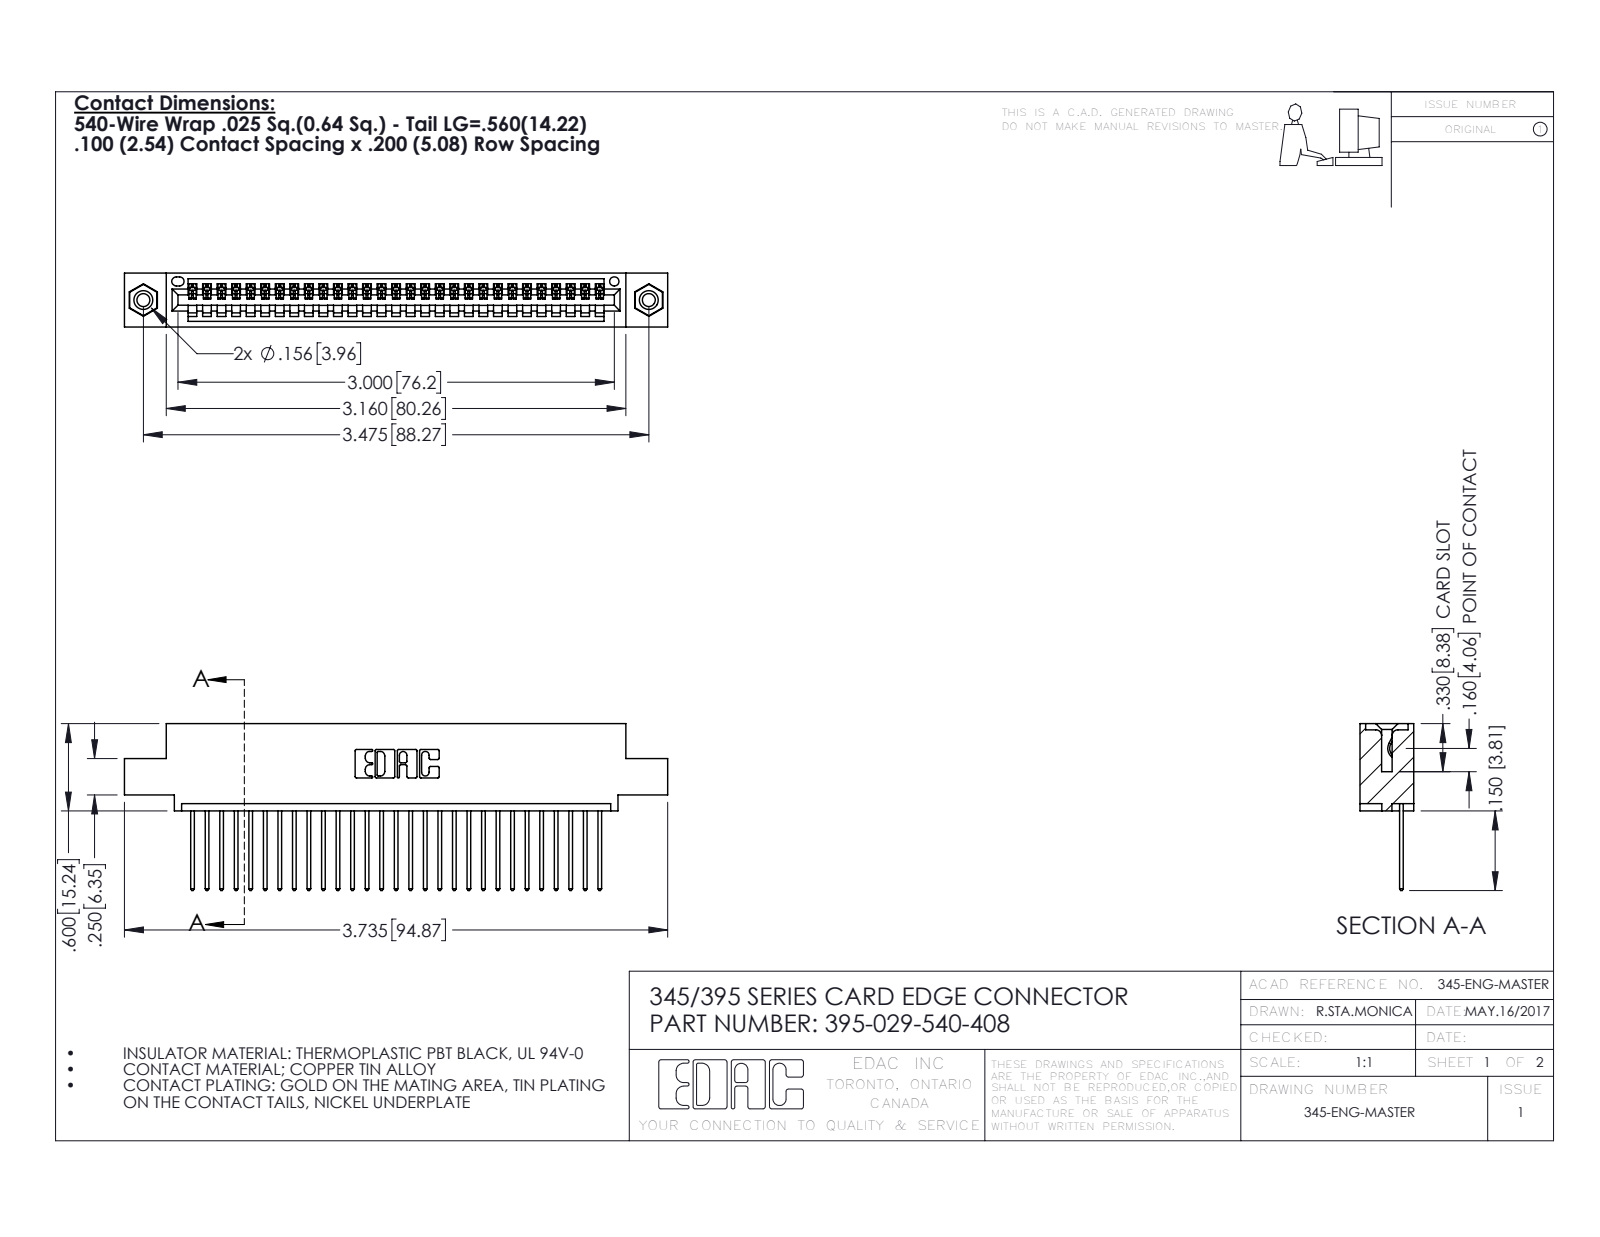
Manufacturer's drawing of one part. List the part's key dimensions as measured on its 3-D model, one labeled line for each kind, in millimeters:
Part name (STEP PRODUCT): 345-292-001_345-293-140; 395-029-540-408; 345-250-001_345-250-003-102; 345 Part_0.110 Offset - 0.156 Dia-TI
STEP written by: SolidWorks 2016 (CONFIG_CONTROL_DESIGN)
Units: millimetres
Bodies: 32 solids, 1872 faces (1276 planar, 580 cylindrical, 16 other)
Overall size (bounding box): 94.9 × 29.1 × 9.4
Volume: 8 870 mm³ · Surface area: 11 990 mm²
Round holes (diameter × count): ⌀2.3 ×2, ⌀3.2 ×2, ⌀4 ×2, ⌀1.6 ×1
Round bosses / shafts (diameter × count): ⌀3.9 ×2
Partial cylindrical surfaces — rounded edges, fillets, slot ends (radius × count): R0.2 ×58, R0.3 ×58, R0.3 ×22, R0.2 ×6, R0.8 ×6, R0.7 ×3, R0.8 ×2, R1 ×2
Main face-to-face distances: 1.8, 7.6, 9.4, 5.1, 2.5, 6.9, 0.6, 5.7, 3.8, 1.8
Hole centre spacings: 6.9, 82.3, 88.3
